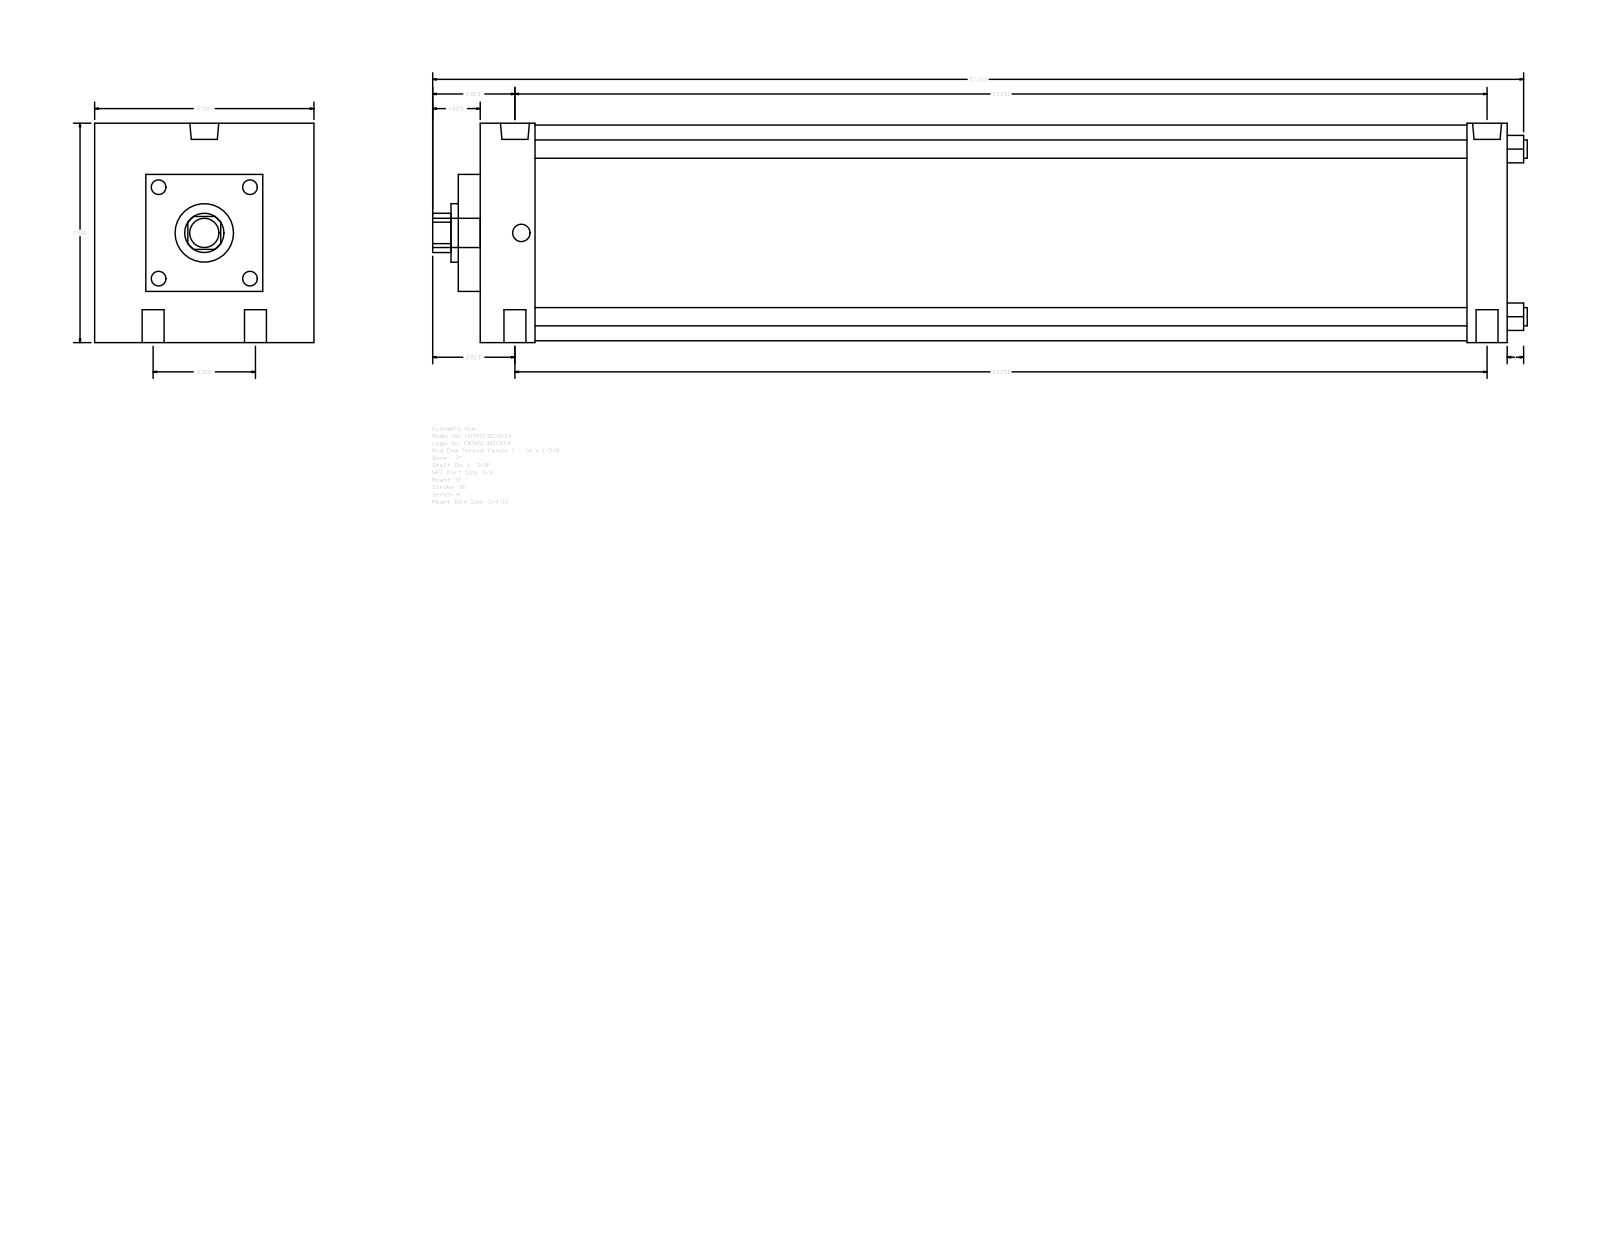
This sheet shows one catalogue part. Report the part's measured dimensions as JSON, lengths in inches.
{"part_name": "A_SF__0700_1.375", "step_written_by": "GSSL Pune (CONFIG_CONTROL_DESIGN)", "units": "inches", "bodies": {"solids": 0, "faces": 93, "planar": 67, "cylindrical": 26, "other": 0}, "overall_size": [37.437, 7.5, 7.5], "round_holes": [[0.75, 4], [0.594, 2], [0.989, 2], [1.375, 1], [2, 1]], "round_bosses_or_shafts": [[0.625, 4], [7.375, 1], [1, 1]], "partial_cylinders_radius": [[0.672, 1]], "face_to_face_distances": [7.5, 35.125, 0.75, 35.875, 2.625, 34.5, 1.875, 33.75, 31.875, 33.25], "hole_center_spacings": [1.75, 33.296, 33.25, 3.5, 33.434, 32.812]}
